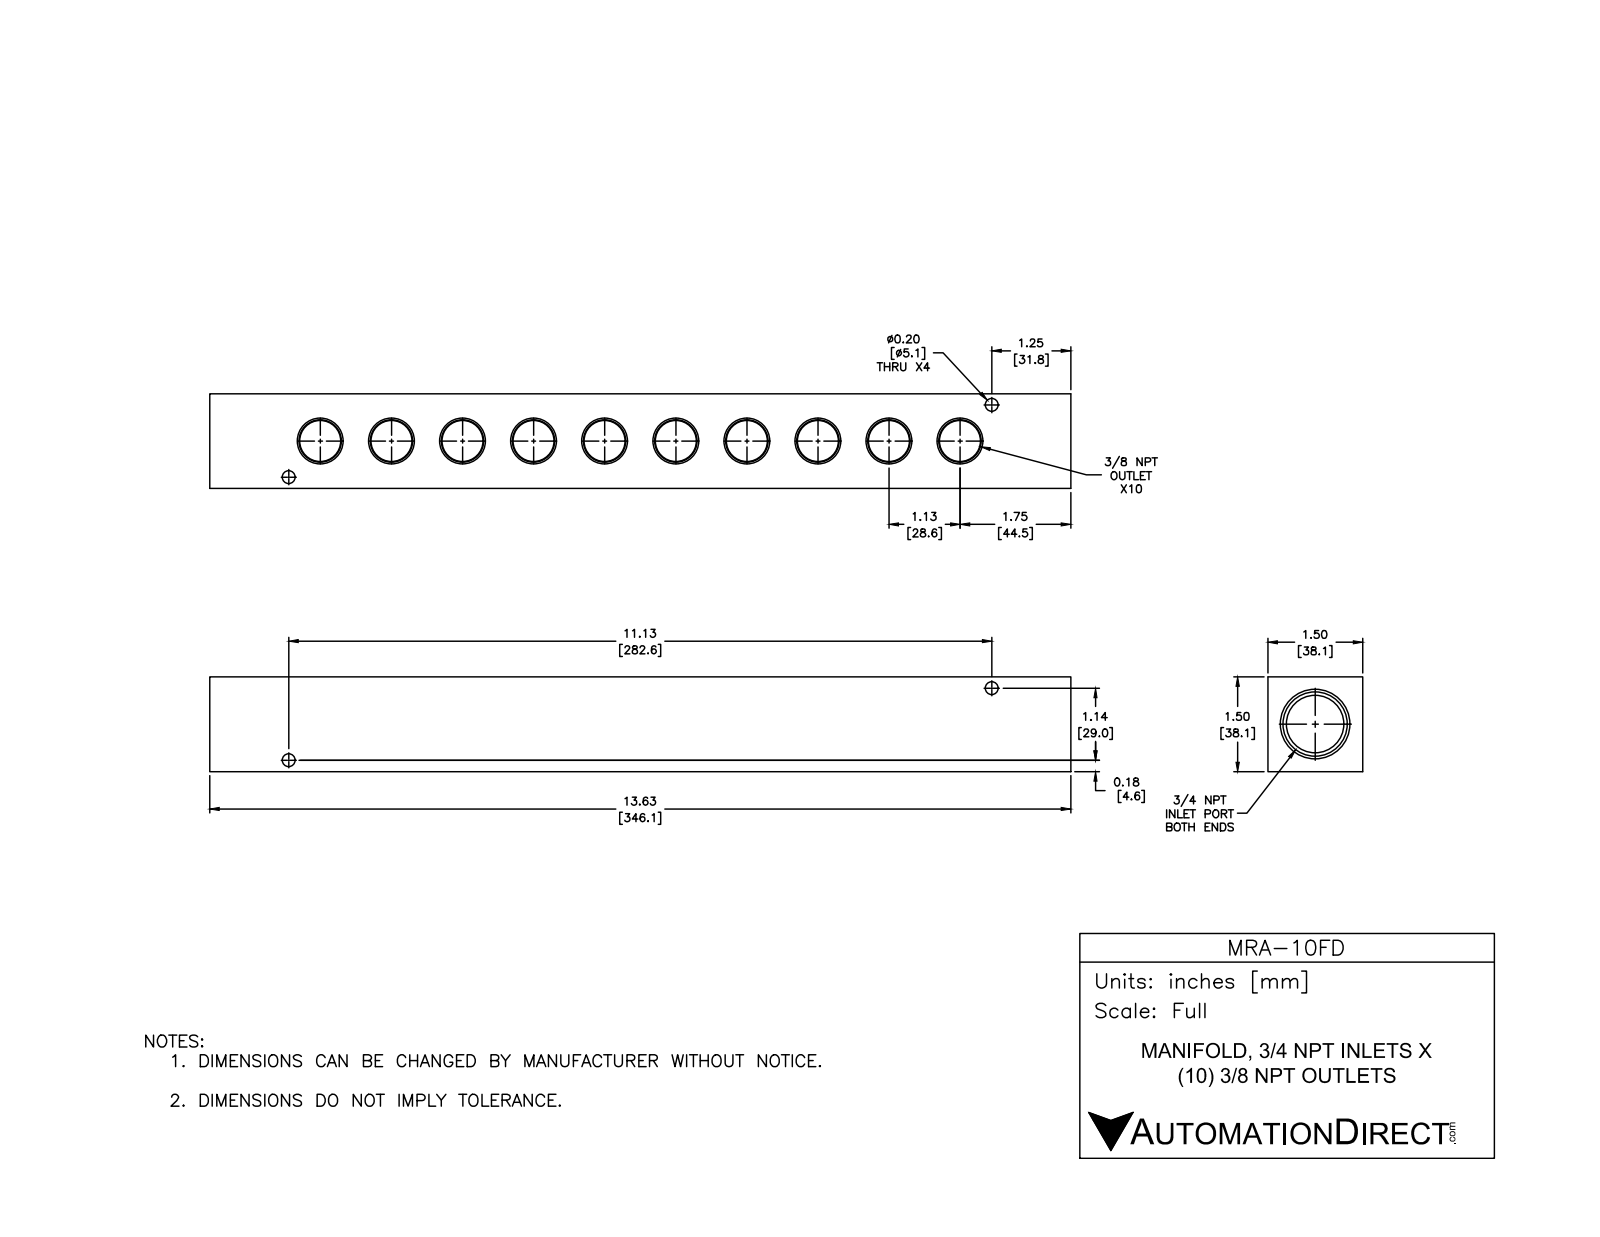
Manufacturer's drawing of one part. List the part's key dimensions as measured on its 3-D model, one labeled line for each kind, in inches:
Part name (STEP PRODUCT): MRA-10FD
STEP written by: SolidWorks 2015 (CONFIG_CONTROL_DESIGN)
Units: inches
Bodies: 1 solid, 94 faces (28 planar, 18 cylindrical, 48 other)
Overall size (bounding box): 13.625 × 1.5 × 1.5
Volume: 20.32 in³ · Surface area: 127.4 in²
Round holes (diameter × count): ⌀0.2 ×4, ⌀0.906 ×1
Main face-to-face distances: 1.5, 13.625, 0.55, 13.075, 12.525, 1.09, 0.41
Hole centre spacings: 11.183
